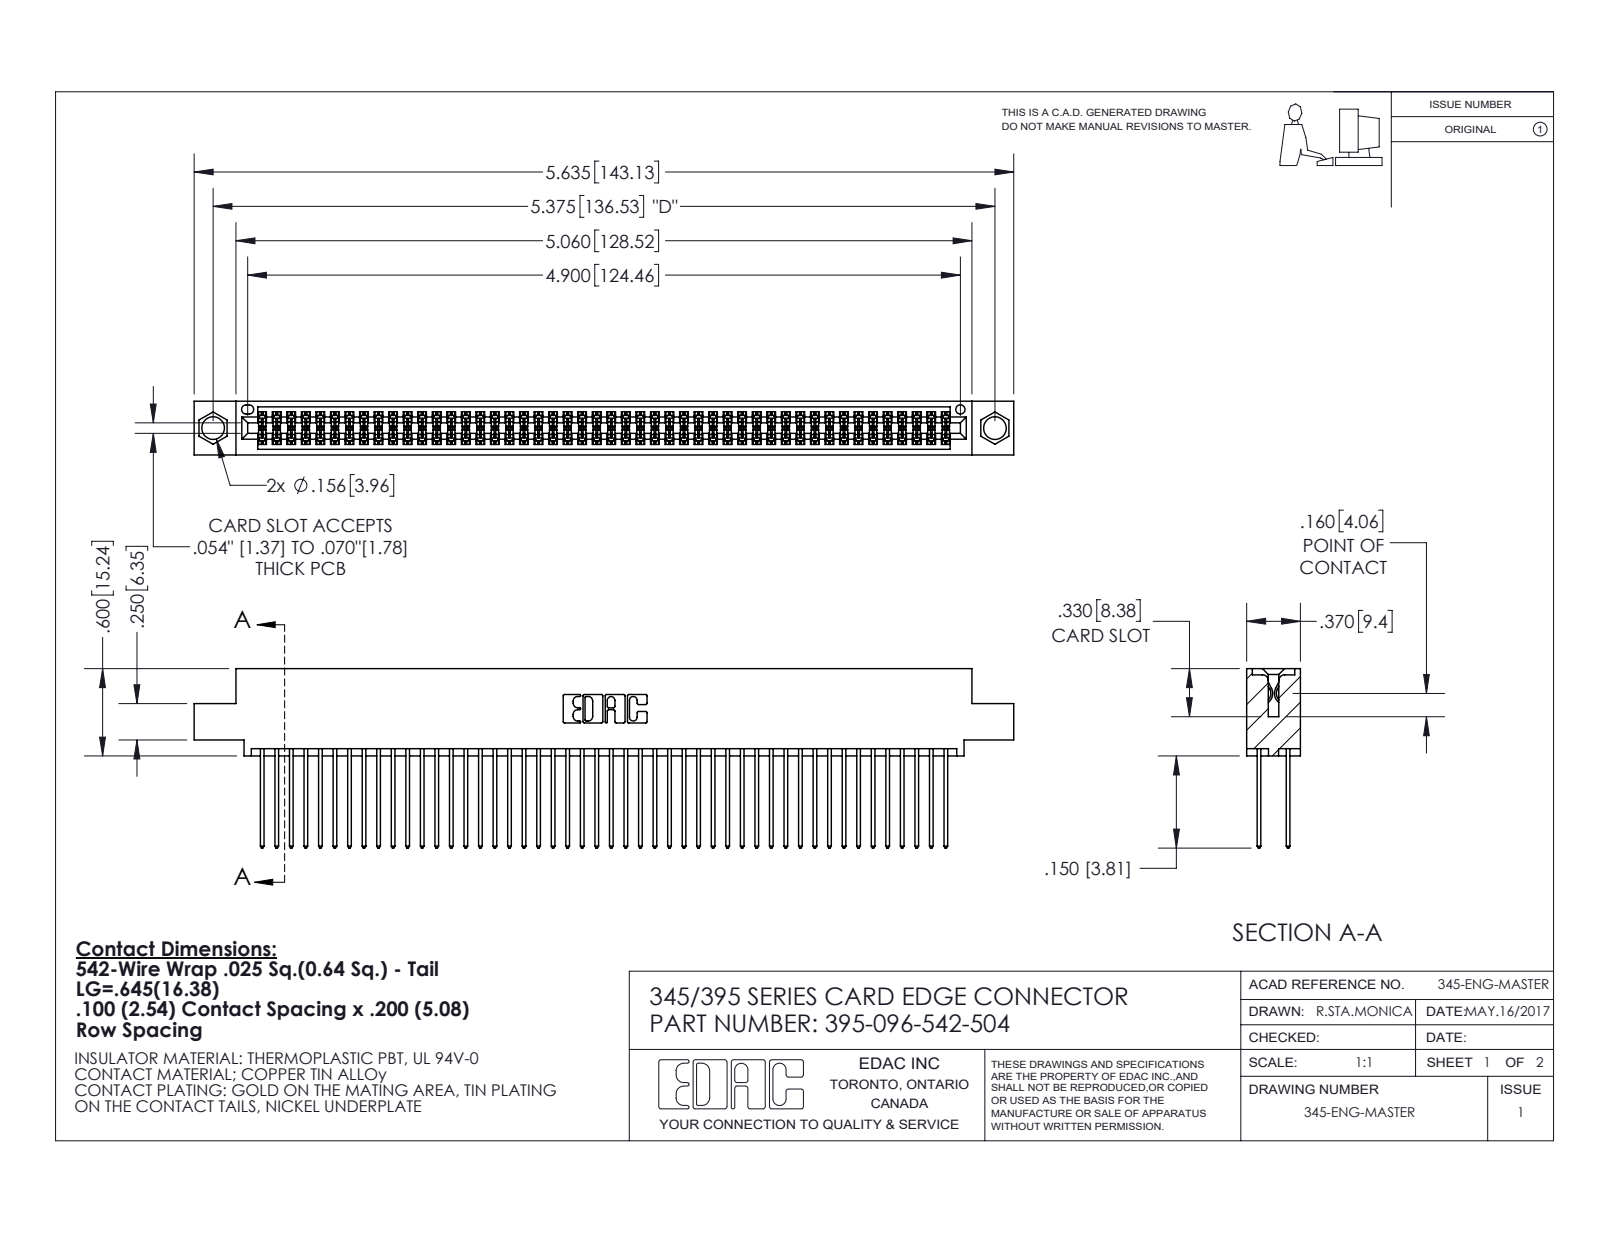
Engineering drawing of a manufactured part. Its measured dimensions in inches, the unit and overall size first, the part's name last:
Units: inches
Overall size (bounding box): 5.635 × 1.232 × 0.37
Round holes (diameter × count): ⌀0.156 ×2, ⌀0.064 ×1
Partial cylindrical surfaces — rounded edges, fillets, slot ends (radius × count): R0.006 ×144, R0.01 ×96, R0.01 ×22, R0.007 ×6, R0.031 ×6, R0.026 ×3, R0.014 ×2, R0.019 ×2
Main face-to-face distances: 0.298, 0.072, 0.2, 0.098, 0.272, 0.025, 0.225, 0.37, 0.175, 0.149
Hole centre spacings: 0.27, 5.139, 5.375
Volume: 0.868 in³ · Surface area: 35.93 in²
Bodies: 97 solids, 4944 faces (3266 planar, 1678 cylindrical, 0 other)
Part name (STEP PRODUCT): 345-292-001_345-293-142; 345 Part_0.110 Offset - 0.156 Dia-TI; 395-096-542-504
STEP written by: SolidWorks 2020 (CONFIG_CONTROL_DESIGN)
